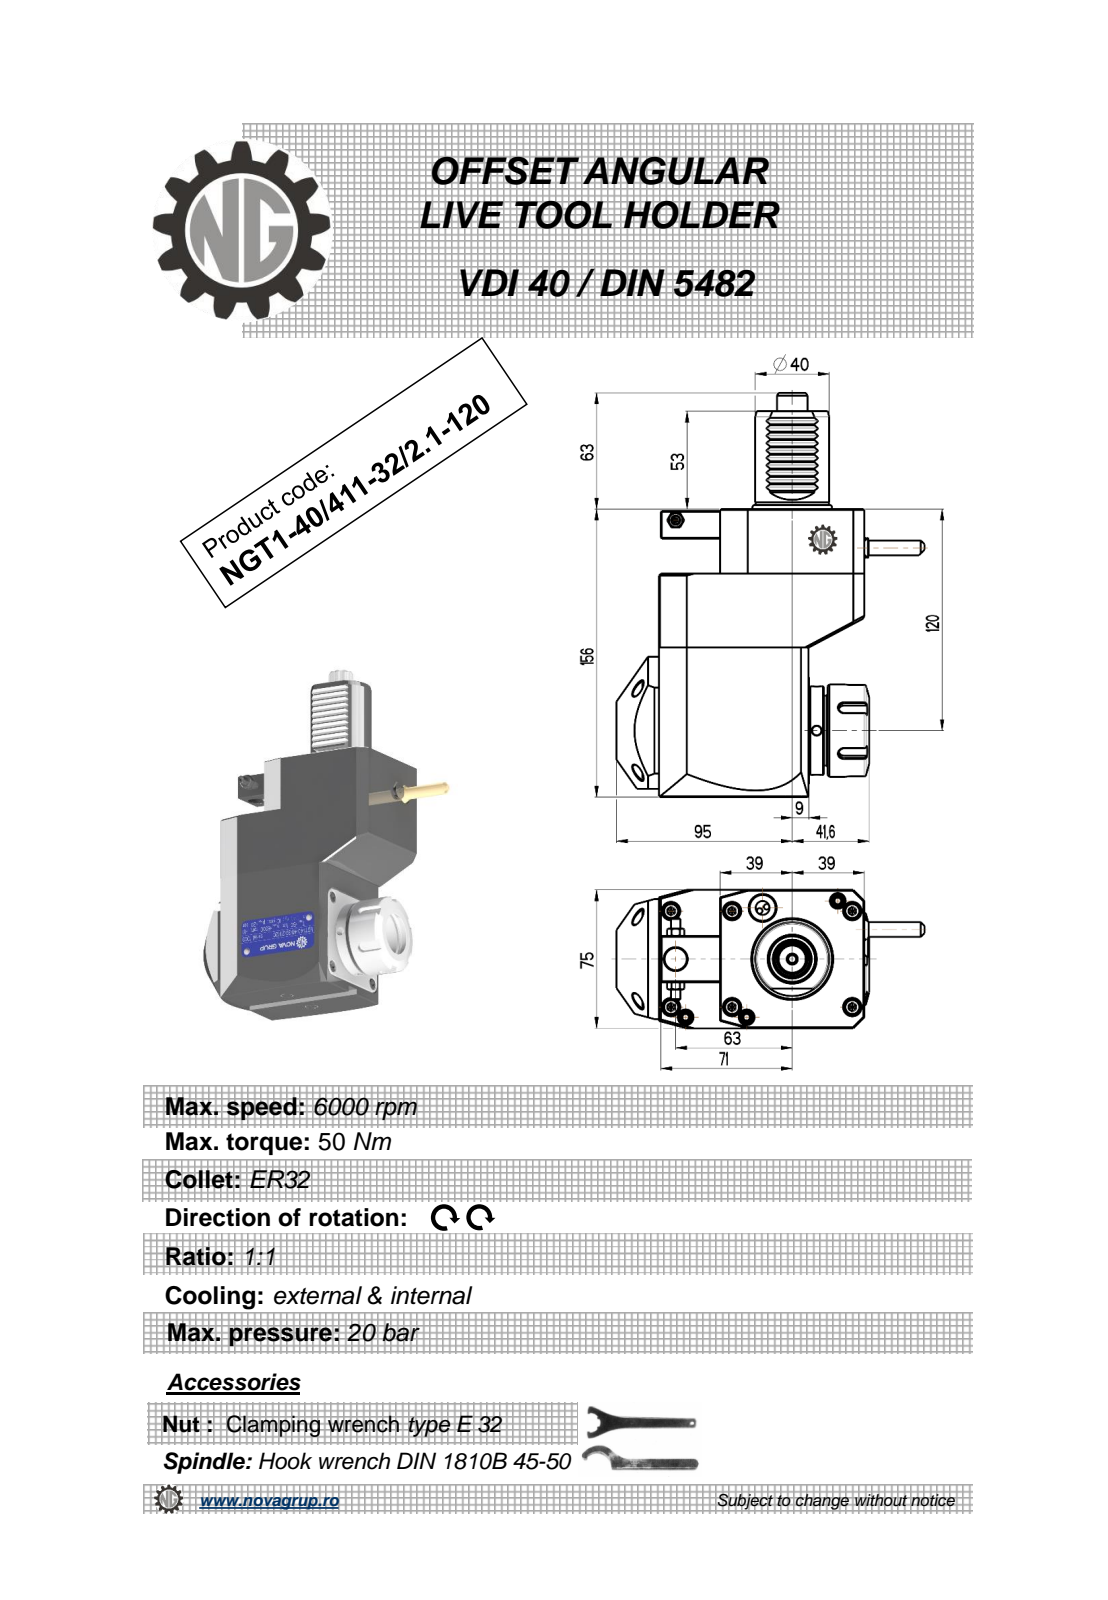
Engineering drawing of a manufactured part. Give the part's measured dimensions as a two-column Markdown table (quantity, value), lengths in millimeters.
| quantity | value |
| --- | --- |
| part name | NGT1_40_411_32_2_1_120 |
| STEP written by | PRO/ENGINEER BY PARAMETRIC TECHNOLOGY CORPORATION, 2010280 (CONFIG_CONTROL_DESIGN) |
| units | millimeters |
| bodies | 1 solid, 469 faces (201 planar, 124 cylindrical, 144 other) |
| overall size | 219 × 166.5 × 76.6 |
| volume | 1 192 000 mm³ |
| surface area | 87 603 mm² |
| round holes (diameter × count) | 5 × 3, 4.2 × 2, 3 × 1, 9.5 × 1, 12 × 1, 27 × 1 |
| round bosses / shafts (diameter × count) | 50 × 1, 48 × 1, 41 × 1, 40 × 1, 11.2 × 1, 8.96 × 1, 8 × 1, 5 × 1 |
| partial cylindrical surfaces (radius × count) | 3.03 × 18, 0.26 × 12, 0.3 × 10, 0.22 × 6, 3 × 5, 0.5 × 1, 6.75 × 1, 8.22 × 1 |
| main face-to-face distances | 75, 156, 111, 35, 121, 81, 30, 33, 48, 78 |
| hole center spacings | 13.25, 20.93, 63, 76.25, 100.28, 112.5, 137.15 |
